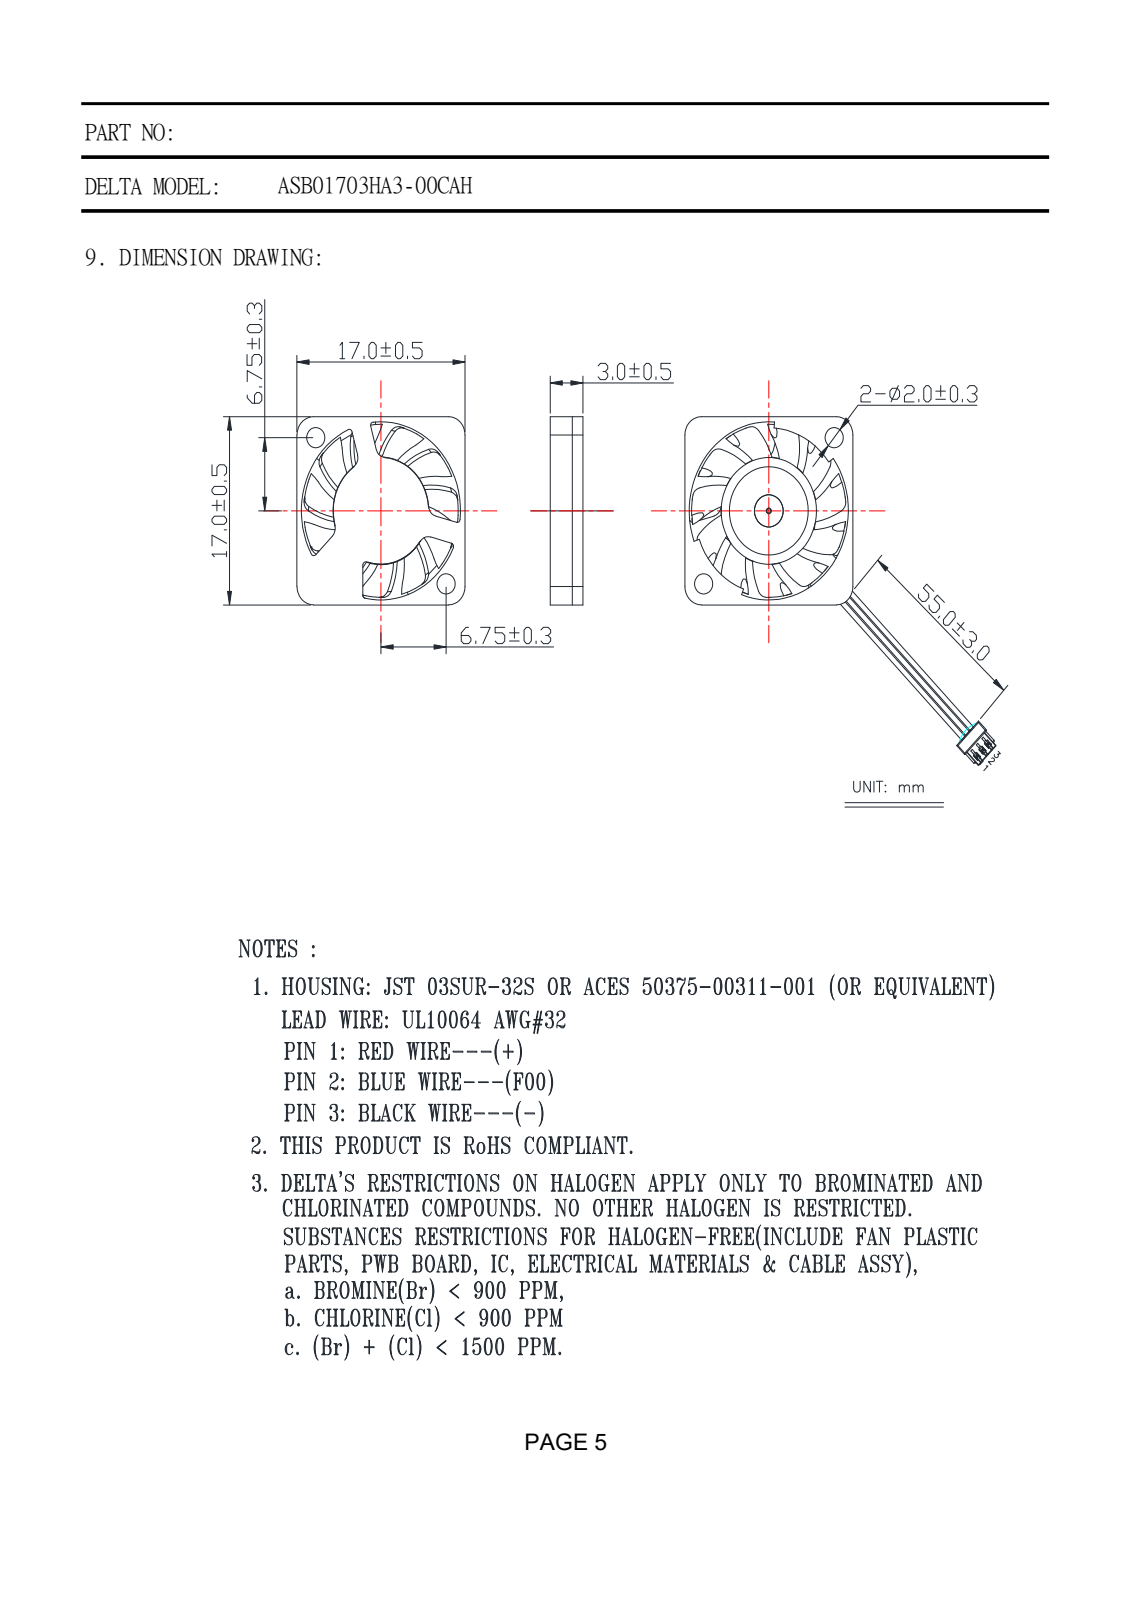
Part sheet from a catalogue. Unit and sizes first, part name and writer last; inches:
Units: inches
Overall size (bounding box): 0.685 × 0.685 × 0.134
Round holes (diameter × count): ⌀0.075 ×2, ⌀0.65 ×1
Round bosses / shafts (diameter × count): ⌀0.39 ×1
Partial cylindrical surfaces — rounded edges, fillets, slot ends (radius × count): R0.012 ×7, R0.039 ×5, R0.008 ×4, R0.067 ×4, R0.079 ×4, R0.02 ×2, R0.315 ×1
Main face-to-face distances: 0.067, 0.091, 0.02, 0.071, 0.685, 0.047, 0.043, 0.024, 0.114, 0.028
Hole centre spacings: 0.376, 0.752
Volume: 0.026 in³ · Surface area: 2.097 in²
Bodies: 3 solids, 168 faces (75 planar, 76 cylindrical, 17 other)
Part name (STEP PRODUCT): IMPELLER; PRT0079; PRT0080; 1703-NEW_ASM
STEP written by: PRO/ENGINEER BY PARAMETRIC TECHNOLOGY CORPORATION, 2009360 (AUTOMOTIVE_DESIGN_CC2)
